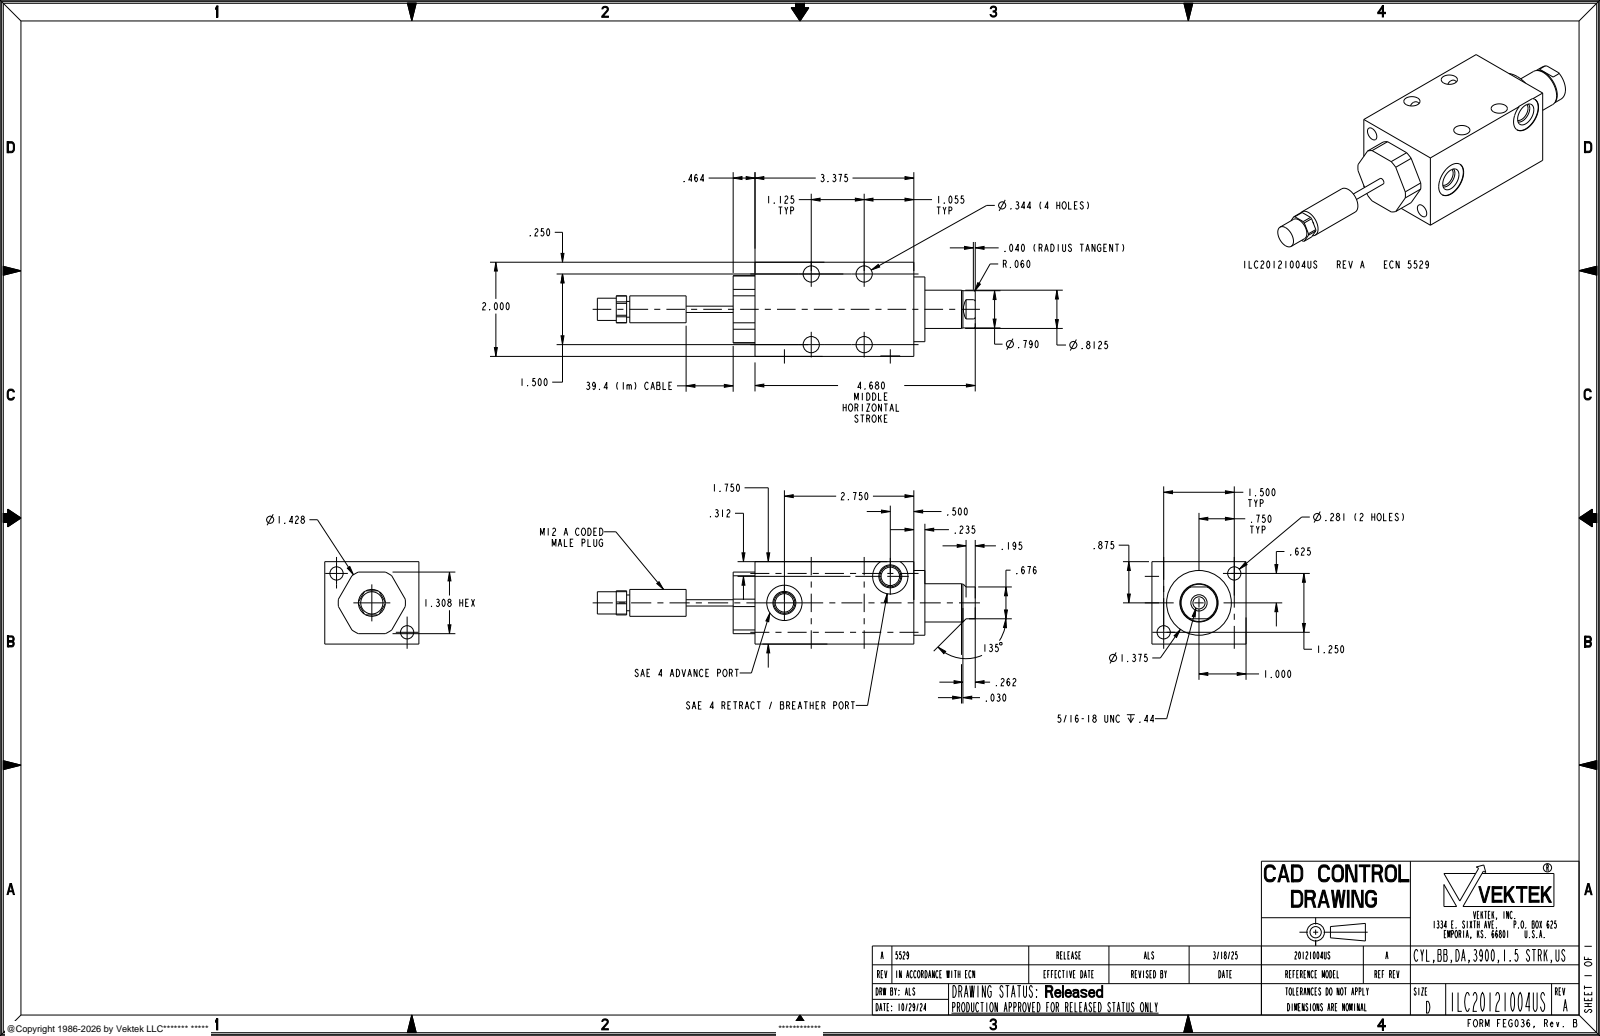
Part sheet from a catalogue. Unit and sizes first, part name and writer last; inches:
Units: inches
Overall size (bounding box): 8.03 × 2.25 × 1.75
Round holes (diameter × count): ⌀0.344 ×4, ⌀0.281 ×2, ⌀0.392 ×2, ⌀0.75 ×2, ⌀0.257 ×1
Round bosses / shafts (diameter × count): ⌀1.375 ×1, ⌀0.813 ×1, ⌀0.79 ×1, ⌀0.571 ×1, ⌀0.472 ×1, ⌀0.335 ×1, ⌀0.312 ×1, ⌀0.134 ×1
Partial cylindrical surfaces — rounded edges, fillets, slot ends (radius × count): R0.714 ×1
Main face-to-face distances: 1.75, 2, 3.375, 3.839, 0.464, 0.235, 3.61, 4.074, 1.308, 0.221
Hole centre spacings: 0.976, 1.125, 1.5, 1.875, 1.953, 2.319
Volume: 12.65 in³ · Surface area: 55.62 in²
Bodies: 1 solid, 107 faces (36 planar, 57 cylindrical, 14 other)
Part name (STEP PRODUCT): ILC20121004US
STEP written by: CREO PARAMETRIC BY PTC INC, 2021164 (AUTOMOTIVE_DESIGN)
